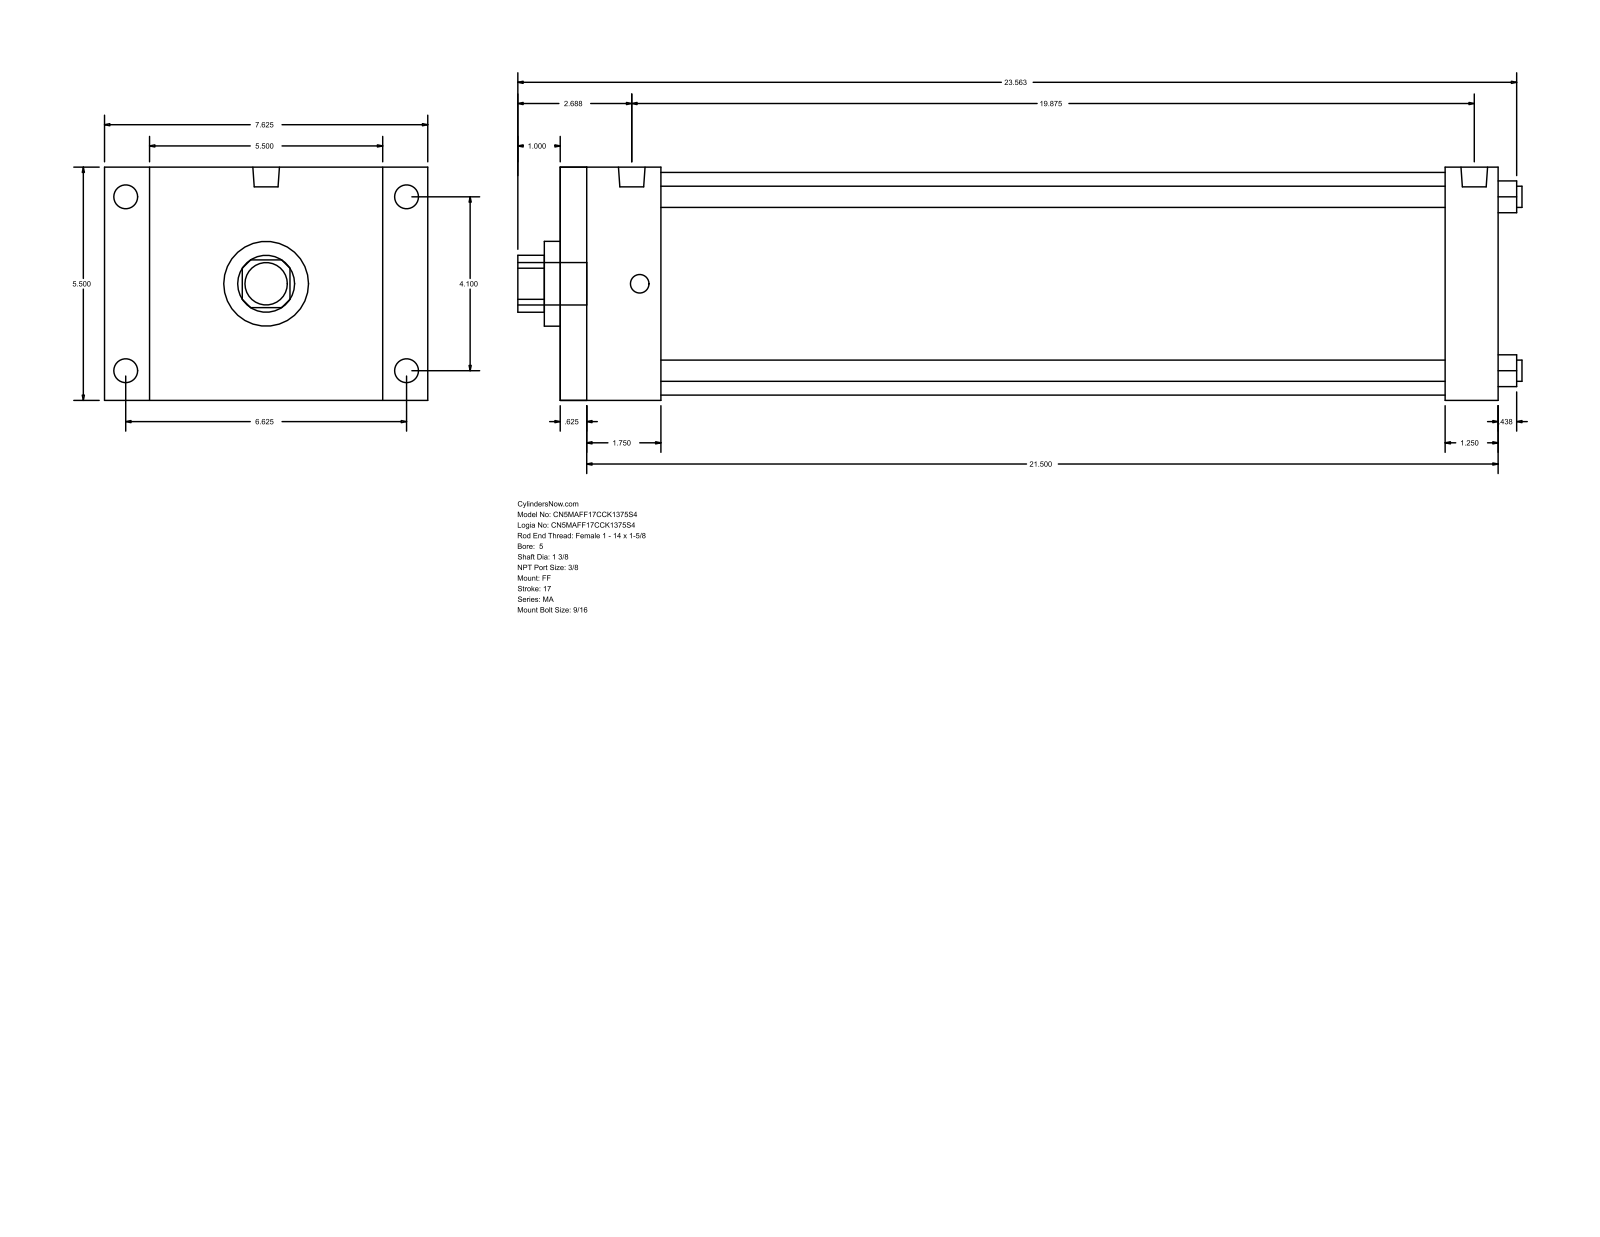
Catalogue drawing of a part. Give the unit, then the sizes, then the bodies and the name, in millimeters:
Units: millimetres
Overall size (bounding box): 601.66 × 193.68 × 139.7
Round holes (diameter × count): ⌀12.7 ×4, ⌀34.92 ×1, ⌀50.8 ×1, ⌀133.35 ×1
Round bosses / shafts (diameter × count): ⌀14.29 ×4, ⌀11.11 ×4, ⌀15.93 ×2, ⌀25.4 ×1
Partial cylindrical surfaces — rounded edges, fillets, slot ends (radius × count): R17.06 ×1
Main face-to-face distances: 139.7, 561.98, 15.87, 546.11, 530.22, 514.35, 31.76, 60.32, 44.45, 469.9
Hole centre spacings: 73.64, 104.14, 147.28
Bodies: 0 solids, 92 faces (64 planar, 28 cylindrical, 0 other)
Part name (STEP PRODUCT): MA_FF__0500_1.375
STEP written by: GSSL Pune (CONFIG_CONTROL_DESIGN)
